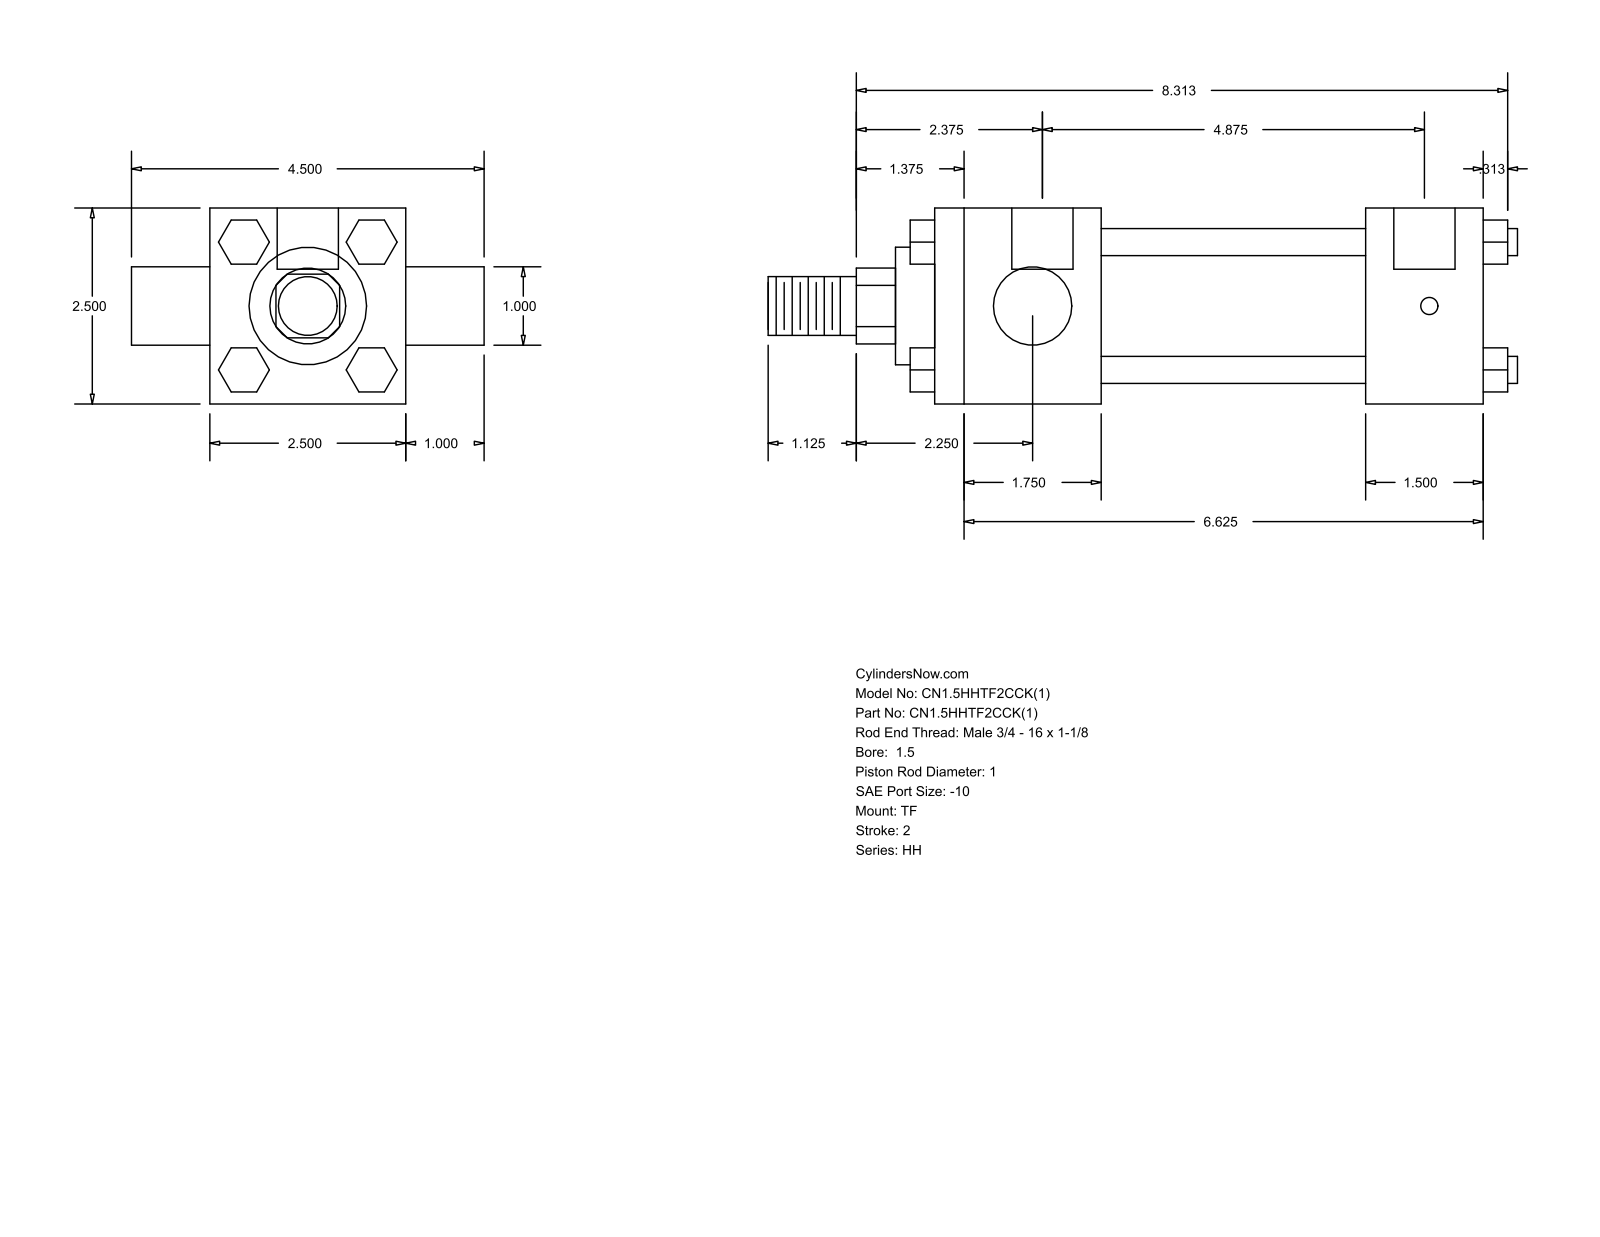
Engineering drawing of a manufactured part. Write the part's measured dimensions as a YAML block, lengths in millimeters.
part_name: "HH_TF__0150_1"
step_written_by: "GSSL Pune (CONFIG_CONTROL_DESIGN)"
units: millimeters
bodies: {solids: 0, faces: 120, planar: 92, cylindrical: 28, other: 0}
overall_size: [242.89, 114.3, 63.5]
round_holes:
  - {diameter: 5.56, count: 3}
  - {diameter: 19.84, count: 2}
round_bosses_or_shafts:
  - {diameter: 8.76, count: 4}
  - {diameter: 25.4, count: 2}
  - {diameter: 44.45, count: 1}
  - {diameter: 38.1, count: 1}
  - {diameter: 19.05, count: 1}
partial_cylinders:
  - {radius: 12.29, count: 1}
face_to_face_distances: [63.5, 38.1, 123.82, 85.72, 53.98, 139.7, 177.8, 25.4, 20.7, 14.29]
hole_center_spacings: [1.59, 125.41, 123.82, 127]
